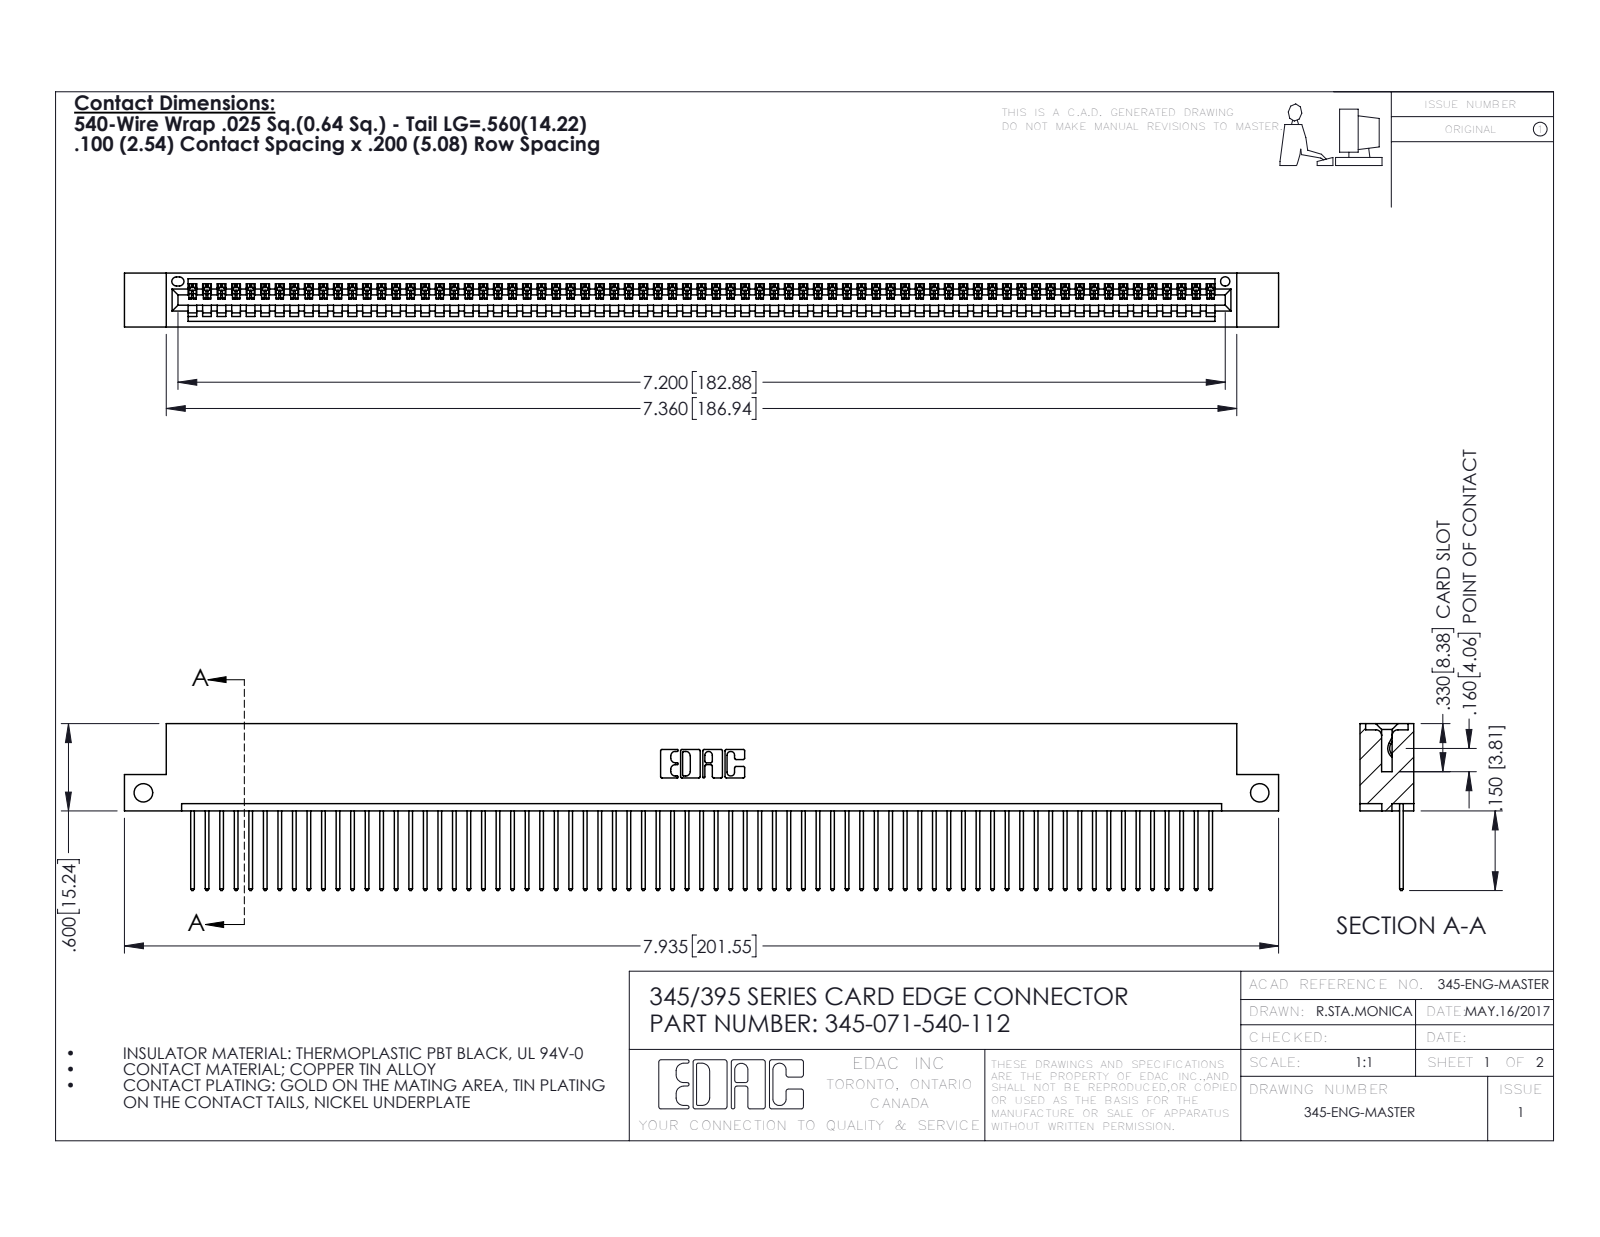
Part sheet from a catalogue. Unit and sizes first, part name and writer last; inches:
Units: inches
Overall size (bounding box): 7.935 × 1.147 × 0.37
Round holes (diameter × count): ⌀0.128 ×2, ⌀0.064 ×1
Partial cylindrical surfaces — rounded edges, fillets, slot ends (radius × count): R0.006 ×142, R0.01 ×142, R0.01 ×22, R0.007 ×6, R0.031 ×6, R0.026 ×3, R0.031 ×2, R0.04 ×2
Main face-to-face distances: 0.072, 0.298, 0.37, 0.098, 0.272, 0.025, 0.2, 0.225, 0.149, 0.072
Hole centre spacings: 7.675
Volume: 1.183 in³ · Surface area: 41.4 in²
Bodies: 72 solids, 4244 faces (2920 planar, 1324 cylindrical, 0 other)
Part name (STEP PRODUCT): 345 Part_Flush Mounting Lugs - Side Mount; 345-292-001_345-293-140; 345-071-540-112
STEP written by: SolidWorks 2016 (CONFIG_CONTROL_DESIGN)
